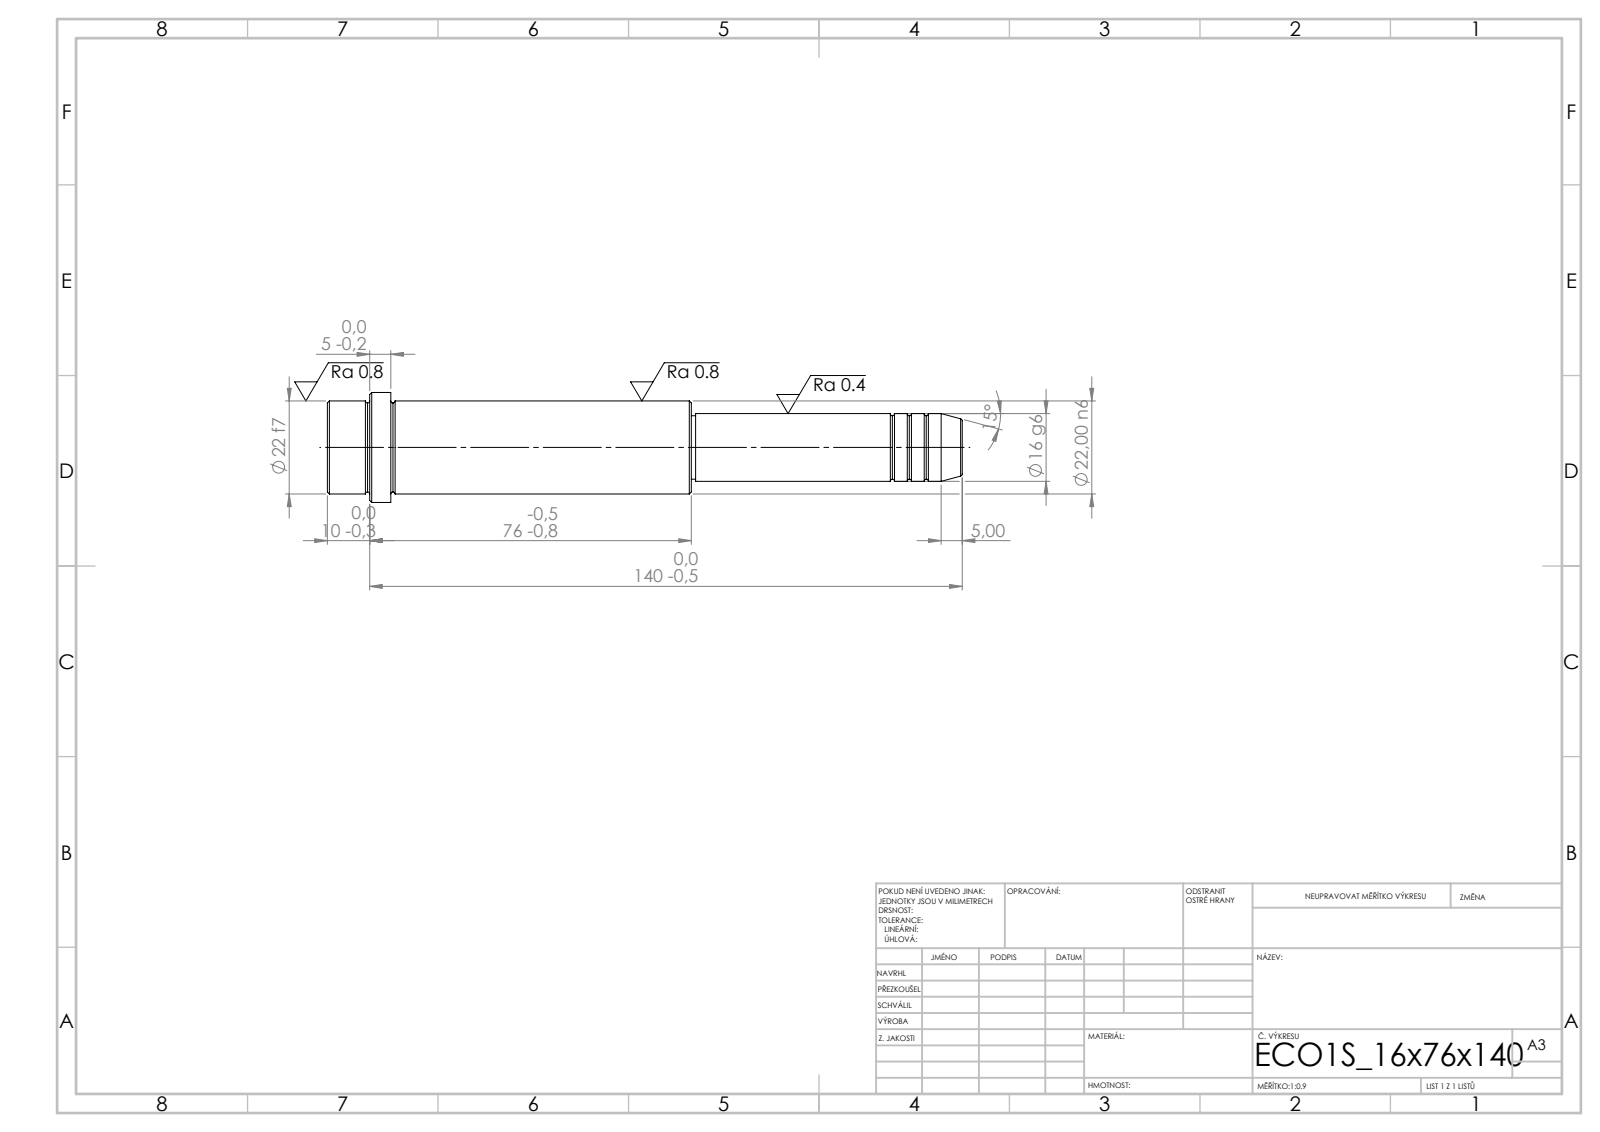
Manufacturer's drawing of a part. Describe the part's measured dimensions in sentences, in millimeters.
Its 3-D file was written by "SolidWorks 2019 (CONFIG_CONTROL_DESIGN)". It is 1 solid with 52 faces: 6 planar, 16 cylindrical and 30 other. Overall it measures 150 by 26 by 26 millimeters. Its volume is 45 991 cubic millimeters and its surface area 10 336 square millimeters. Round bosses or shafts: 1 of diameter 26, 1 of diameter 22, 1 of diameter 16, 1 of diameter 15. The main face-to-face distances are 86, 71, 15, 64, 135, 150, 140, 76, 5, 10.
